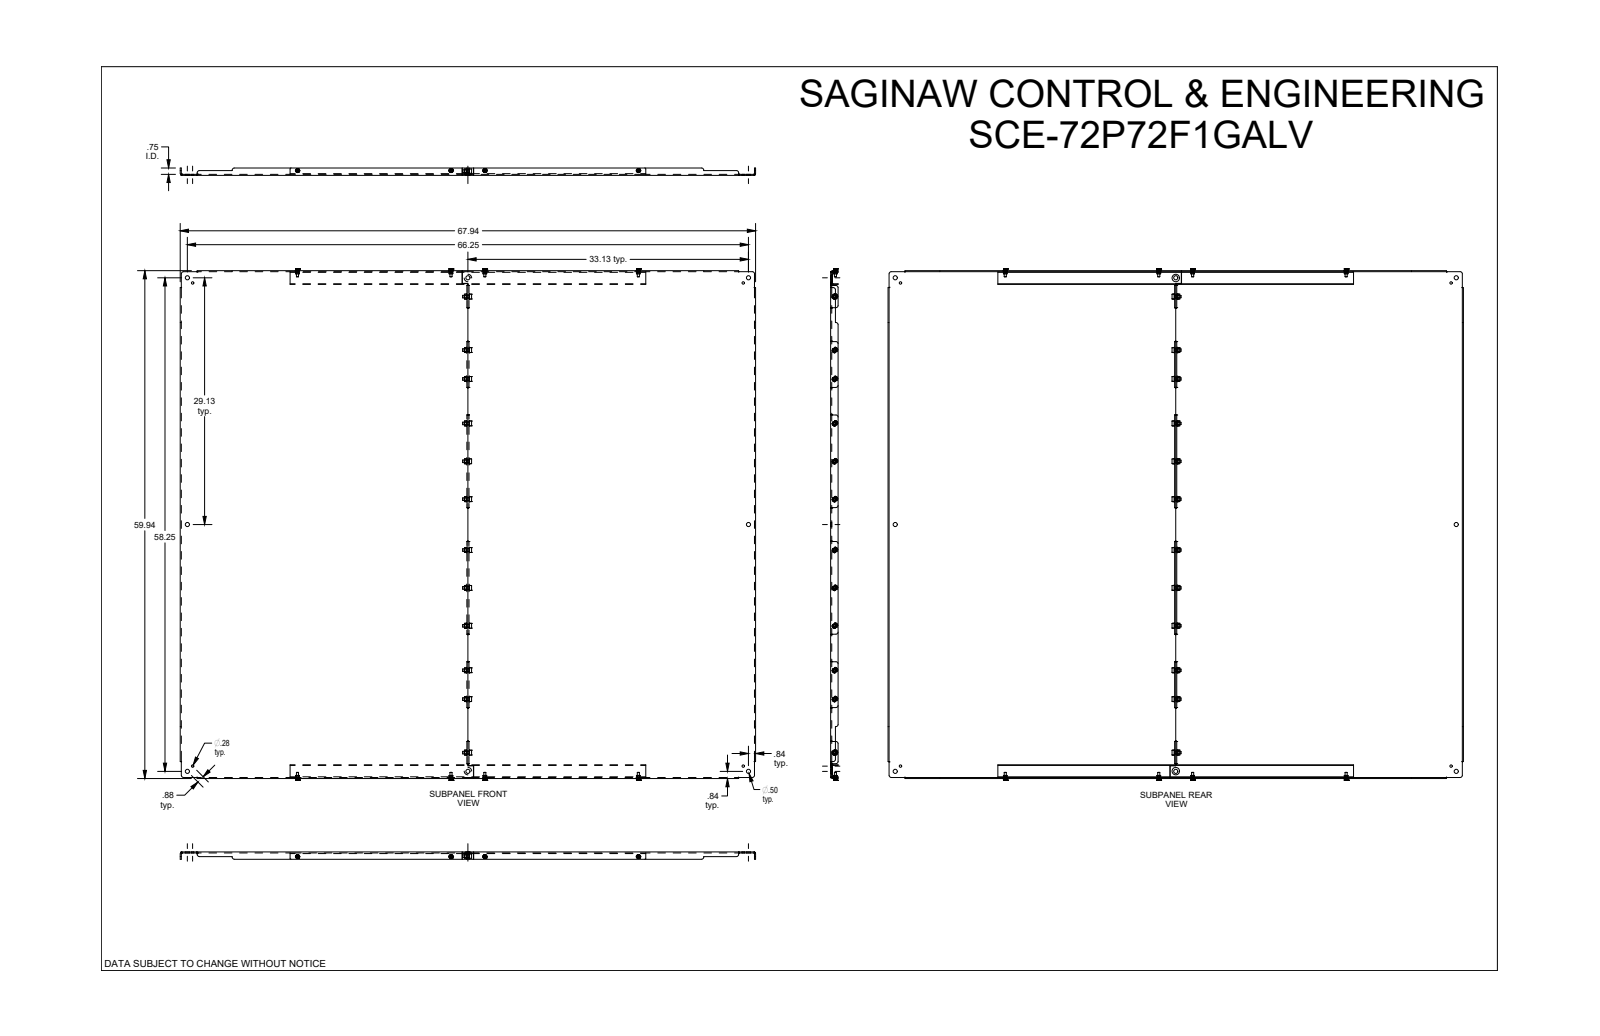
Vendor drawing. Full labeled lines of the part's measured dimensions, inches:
Part name (STEP PRODUCT): SCE-72P72F1GALV
STEP written by: SolidWorks 2019 (CONFIG_CONTROL_DESIGN)
Units: inches
Bodies: 44 solids, 1922 faces (528 planar, 478 cylindrical, 916 other)
Overall size (bounding box): 67.938 × 60.386 × 0.875
Volume: 553.9 in³ · Surface area: 9 114 in²
Round holes (diameter × count): ⌀0.312 ×12, ⌀0.375 ×12, ⌀0.5 ×8, ⌀0.25 ×4, ⌀0.308 ×4, ⌀0.344 ×4, ⌀0.281 ×3, ⌀0.875 ×2, ⌀0.28 ×1
Round bosses / shafts (diameter × count): ⌀0.31 ×12, ⌀0.5 ×4, ⌀0.44 ×4, ⌀0.343 ×4, ⌀0.248 ×4
Partial cylindrical surfaces — rounded edges, fillets, slot ends (radius × count): R0.01 ×200, R0.25 ×24, R0.06 ×16, R0.172 ×8, R0.112 ×6, R0.237 ×6, R0.08 ×4, R0.158 ×4
Main face-to-face distances: 0.125, 0.125, 0.078, 0.203, 33.844, 1.422, 58.187, 0.078, 59.813, 59.687
Hole centre spacings: 29.125, 0.875, 28.513, 32.511, 32.512, 33.125, 33.125, 57.634
